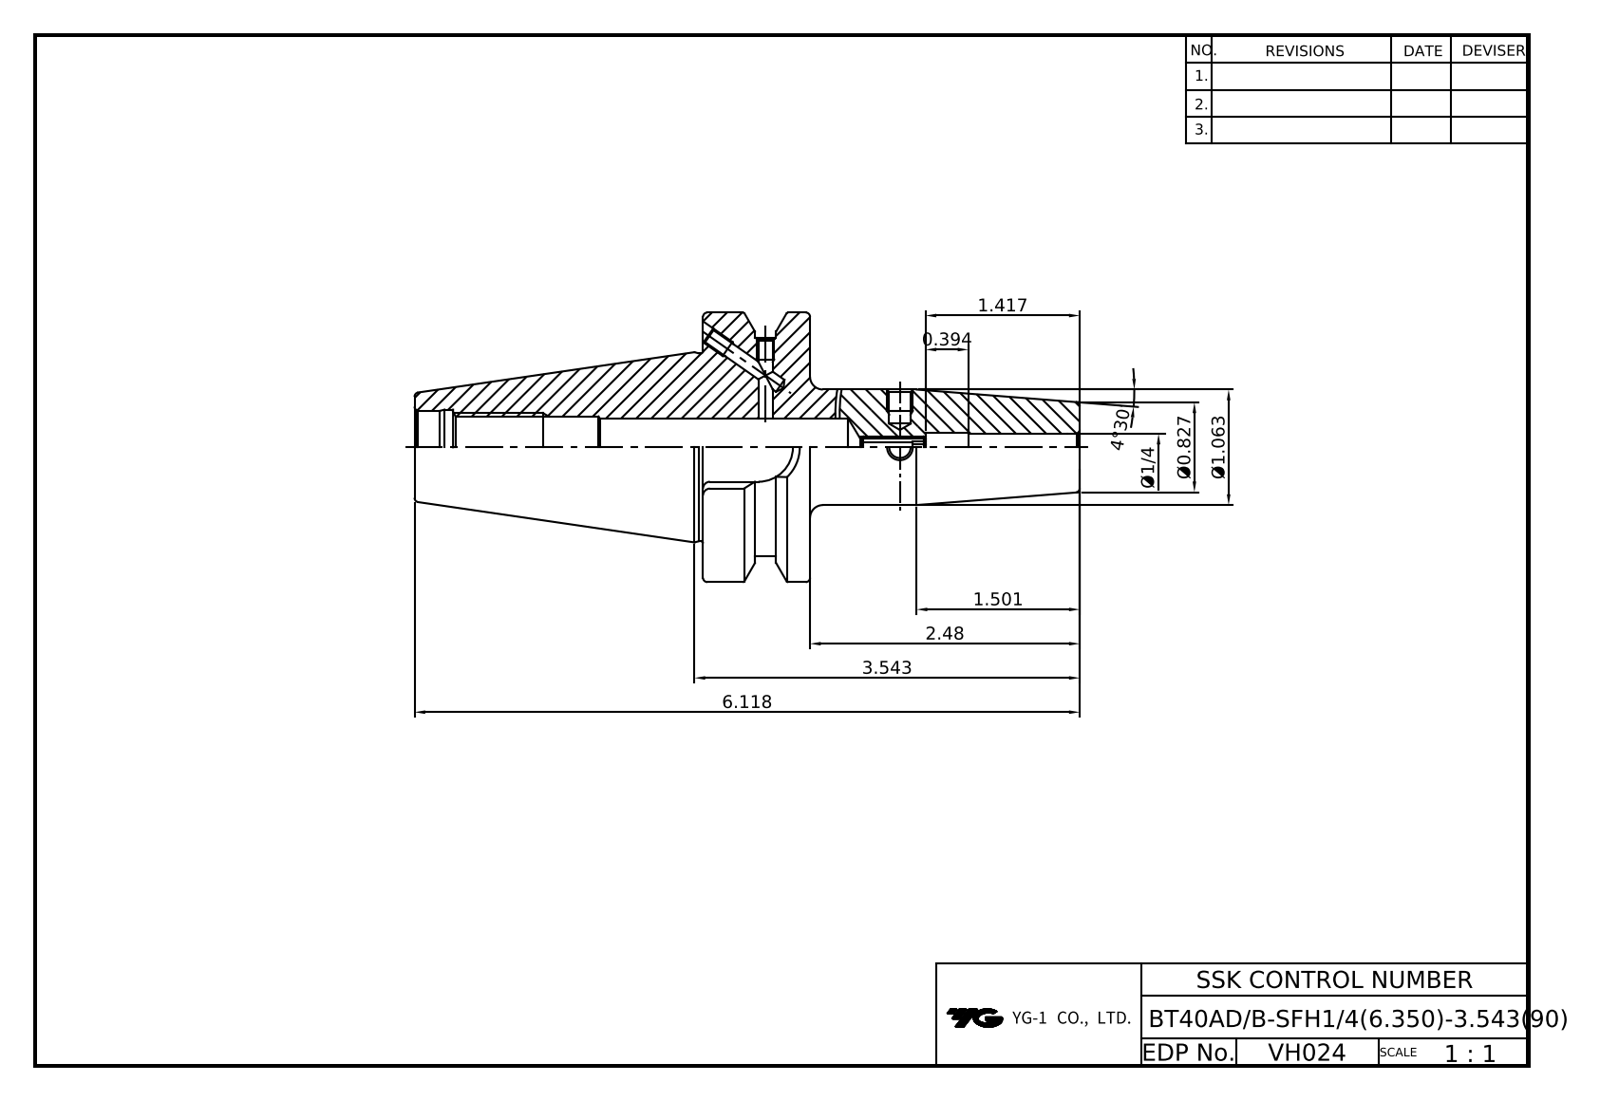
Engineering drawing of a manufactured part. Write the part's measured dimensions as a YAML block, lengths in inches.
part_name: "BT40ADB-SFH4_7625-90"
step_written_by: "CREO PARAMETRIC BY PTC INC, 2018500 (CONFIG_CONTROL_DESIGN)"
units: inches
bodies: {solids: 1, faces: 92, planar: 22, cylindrical: 30, other: 40}
overall_size: [6.118, 2.48, 2.48]
volume: 9.03
surface_area: 46.79
round_holes:
  - {diameter: 0.165, count: 1}
  - {diameter: 0.197, count: 1}
  - {diameter: 0.25, count: 1}
  - {diameter: 0.266, count: 1}
  - {diameter: 0.531, count: 1}
  - {diameter: 0.551, count: 1}
  - {diameter: 0.63, count: 1}
  - {diameter: 0.669, count: 1}
  - {diameter: 0.693, count: 1}
round_bosses_or_shafts:
  - {diameter: 2.48, count: 1}
  - {diameter: 2.008, count: 1}
  - {diameter: 1.732, count: 1}
  - {diameter: 1.063, count: 1}
partial_cylinders:
  - {radius: 0.317, count: 1}
face_to_face_distances: [0.984, 1.78, 3.465, 2.48, 0.673, 0.311, 2.791, 0.476, 0.197, 0.508]
